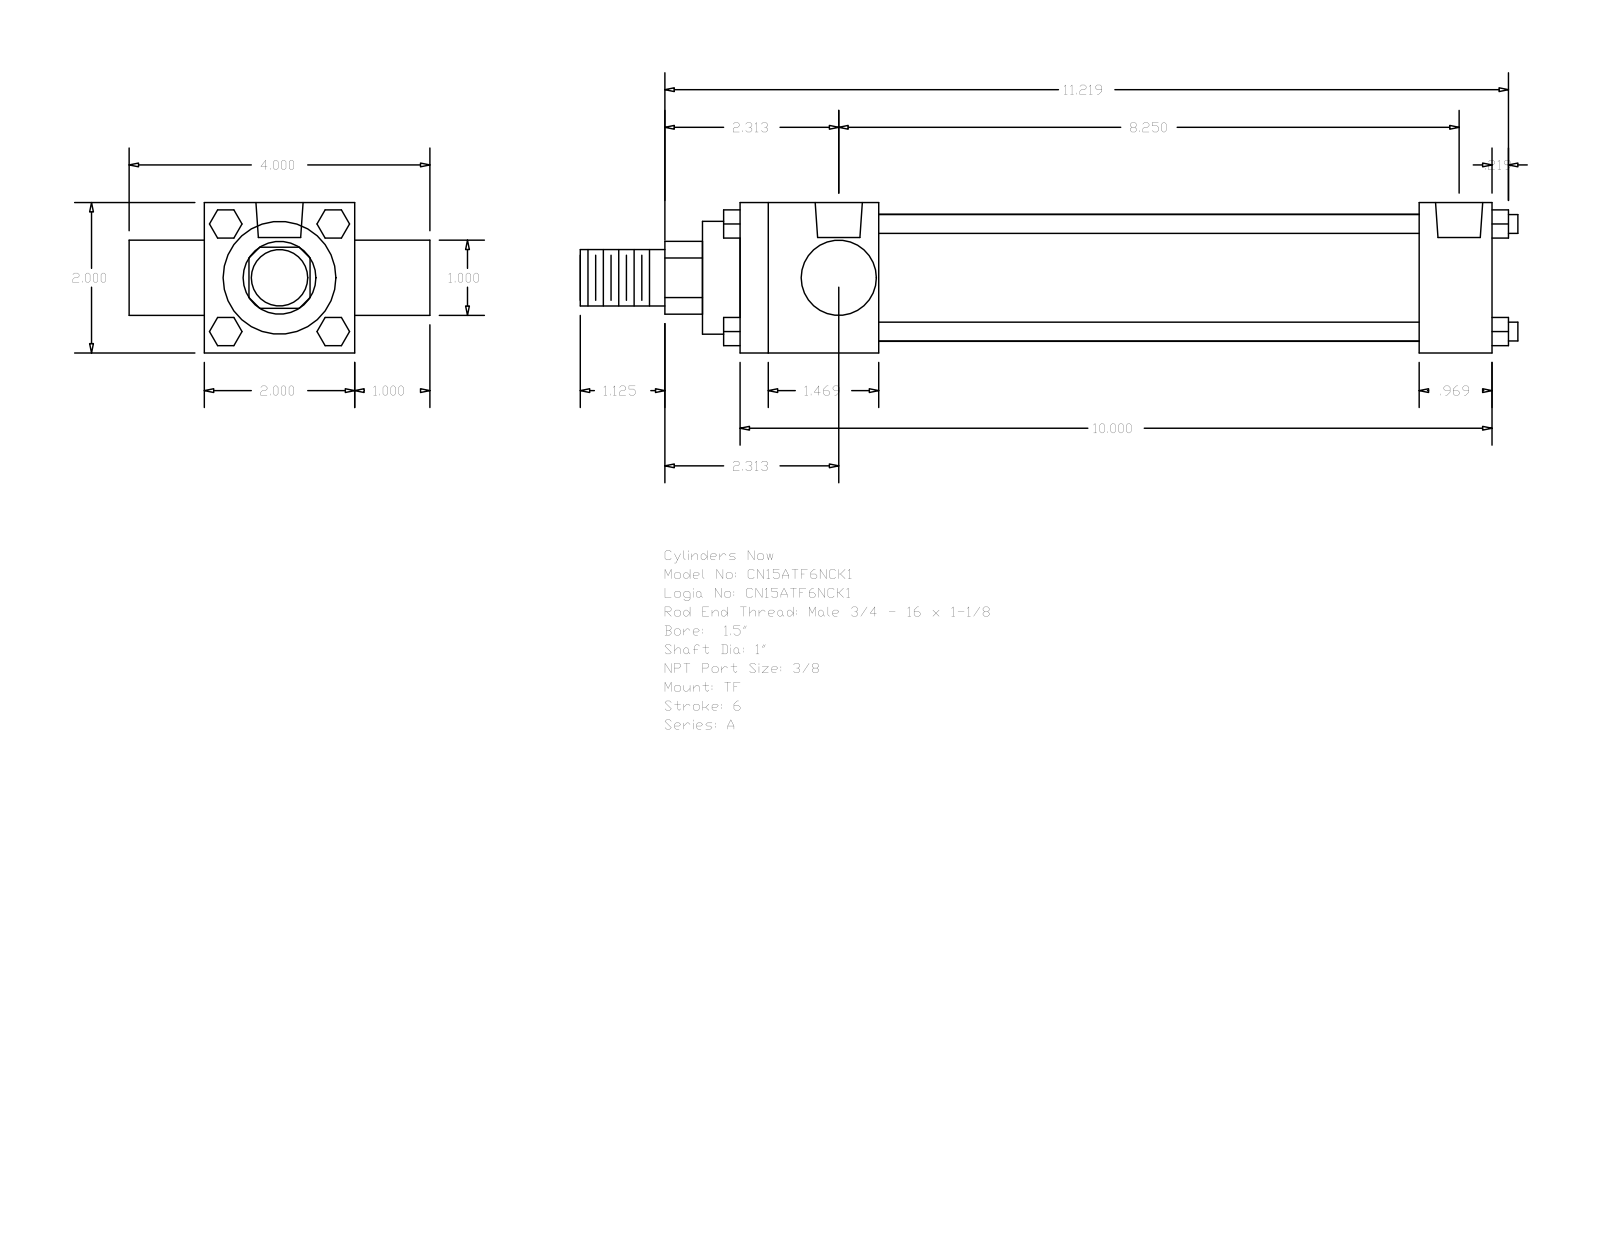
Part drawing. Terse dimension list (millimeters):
name: A_TF__0150_1
written by: GSSL Pune (CONFIG_CONTROL_DESIGN)
unit: mm
bodies: 0 solids, 120 faces (92 planar, 28 cylindrical, 0 other)
size: 316.71 × 101.6 × 50.8
holes: 3× ⌀5.56, 2× ⌀15.93
bosses: 4× ⌀6.35, 2× ⌀25.4, 1× ⌀42.93, 1× ⌀38.1, 1× ⌀19.05
rounds: 1× R12.29
face distances: 50.8, 25.4, 254, 76.2, 46.83, 229.39, 182.56, 207.17, 24.61, 12.7
hole spacings: 3.97, 205.58, 201.61, 209.55
